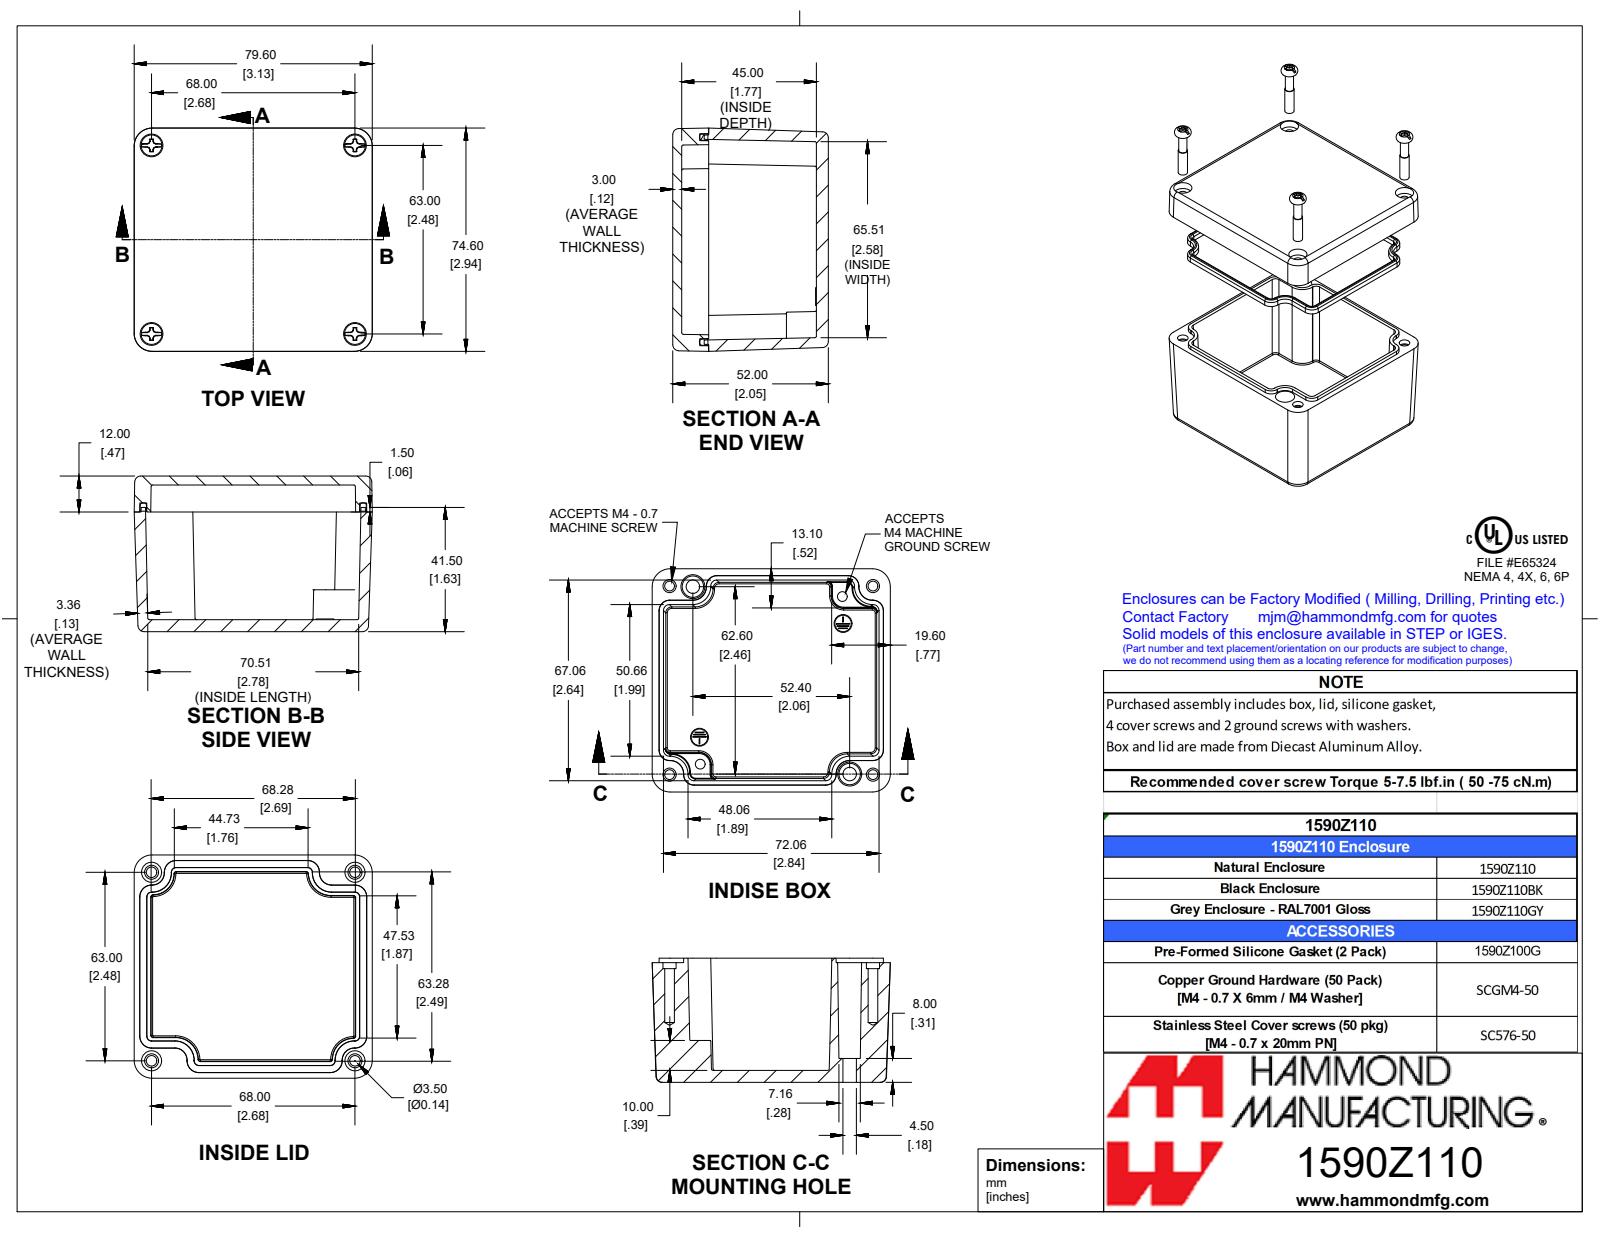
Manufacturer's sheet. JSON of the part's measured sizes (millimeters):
{"part_name": "1590Z110BK", "step_written_by": "SolidWorks 2019 (CONFIG_CONTROL_DESIGN)", "units": "millimeters", "bodies": {"solids": 7, "faces": 527, "planar": 229, "cylindrical": 120, "other": 178}, "overall_size": [79.6, 74.6, 52], "volume_mm3": 103100, "surface_area_mm2": 58780, "round_holes": [[3.3, 6], [3.5, 4], [4.4, 4], [4.7, 4], [7.6, 4], [4.5, 2], [5.5, 2]], "round_bosses_or_shafts": [[3.9, 4], [3.4, 4], [6, 2]], "partial_cylinders_radius": [[0.5, 18], [2, 16], [0.8, 12], [6, 12], [0.3, 10], [3.5, 8], [1.5, 4], [4.5, 4]], "face_to_face_distances": [52, 3, 49, 4, 48, 45, 9, 36, 40, 12], "hole_center_spacings": [7.8, 9, 10.8, 16, 50.1, 50.3, 51.5, 51.7]}
